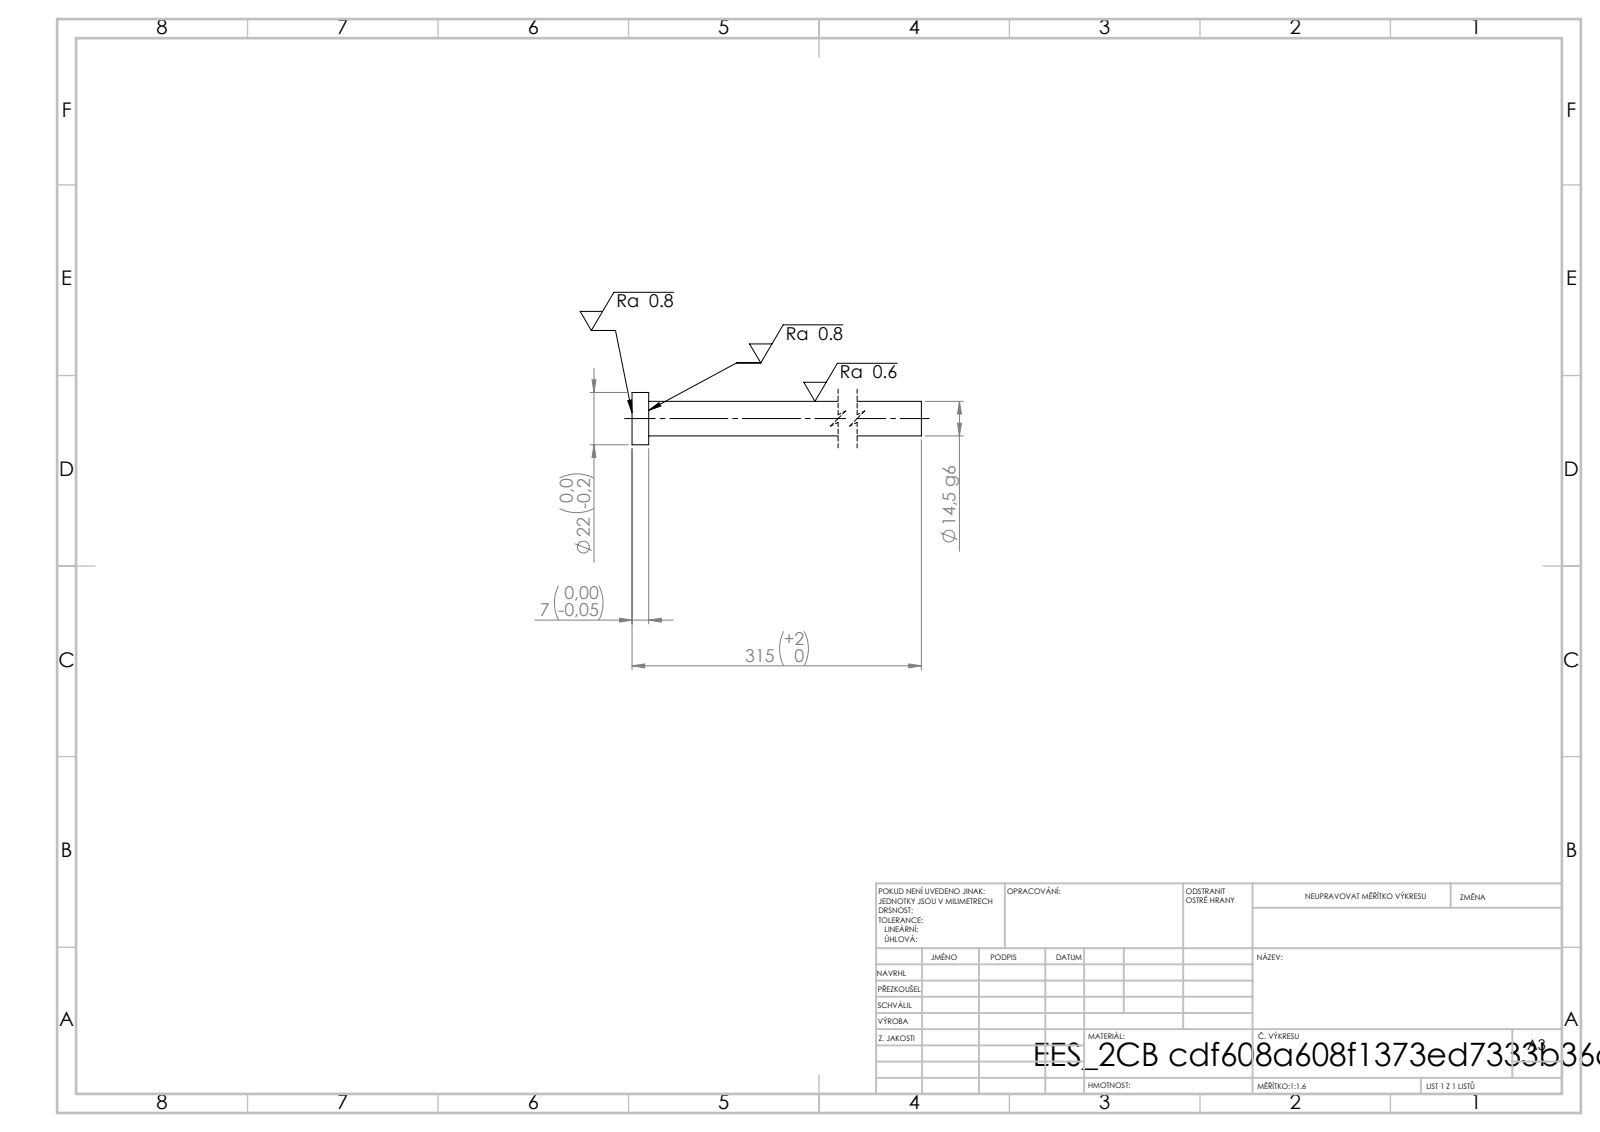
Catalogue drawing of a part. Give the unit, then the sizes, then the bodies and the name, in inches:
Units: inches
Overall size (bounding box): 12.402 × 0.866 × 0.866
Round bosses / shafts (diameter × count): ⌀0.866 ×1, ⌀0.571 ×1
Main face-to-face distances: 0.276, 12.402, 12.126
Volume: 3.266 in³ · Surface area: 23.67 in²
Bodies: 1 solid, 7 faces (3 planar, 4 cylindrical, 0 other)
STEP written by: SolidWorks 2019 (CONFIG_CONTROL_DESIGN)
